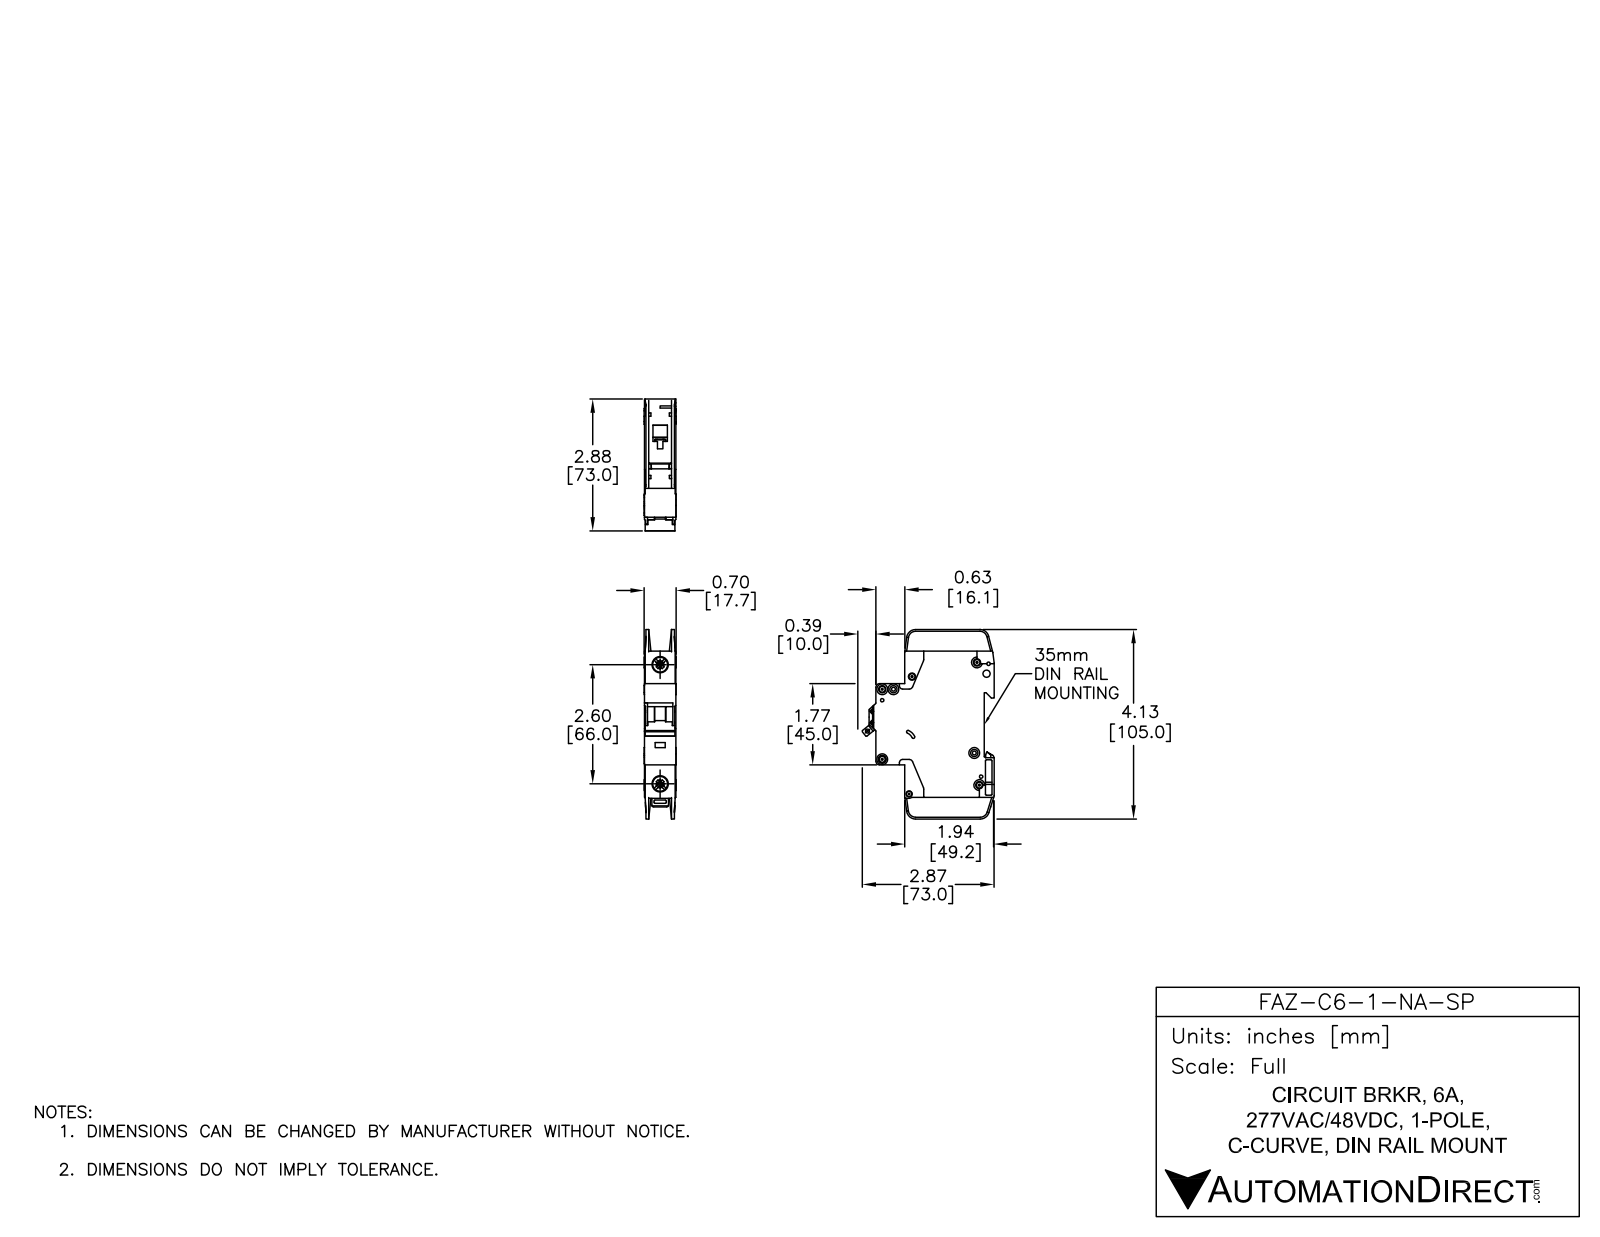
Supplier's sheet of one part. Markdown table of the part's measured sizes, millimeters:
| quantity | value |
| --- | --- |
| part name | FAZ-C6-1-NA-SP |
| STEP written by | SolidWorks 2014 (AUTOMOTIVE_DESIGN) |
| units | millimeters |
| bodies | 3 solids, 784 faces (409 planar, 263 cylindrical, 112 other) |
| overall size | 105 × 73.04 × 17.7 |
| volume | 77 695 mm³ |
| surface area | 24 740 mm² |
| round holes (diameter × count) | 3.6 × 7, 1.09 × 2, 1.5 × 2, 4 × 2, 7.15 × 2, 8.2 × 2, 1.9 × 1, 2.15 × 1, 2.2 × 1, 2.55 × 1, 3.3 × 1, 3.4 × 1 |
| round bosses / shafts (diameter × count) | 6 × 7, 2.5 × 1 |
| partial cylindrical surfaces (radius × count) | 0.25 × 29, 0.5 × 18, 1 × 10, 2 × 10, 5 × 5, 4 × 4, 1.8 × 3, 0.2 × 2 |
| main face-to-face distances | 17.5, 15.05, 0.7, 2.45, 1.75, 15.75, 13.3, 14, 12.6, 2 |
| hole center spacings | 6.2, 5.19, 6.1, 8.19, 8.56, 8.7, 11.11, 12.45 |
